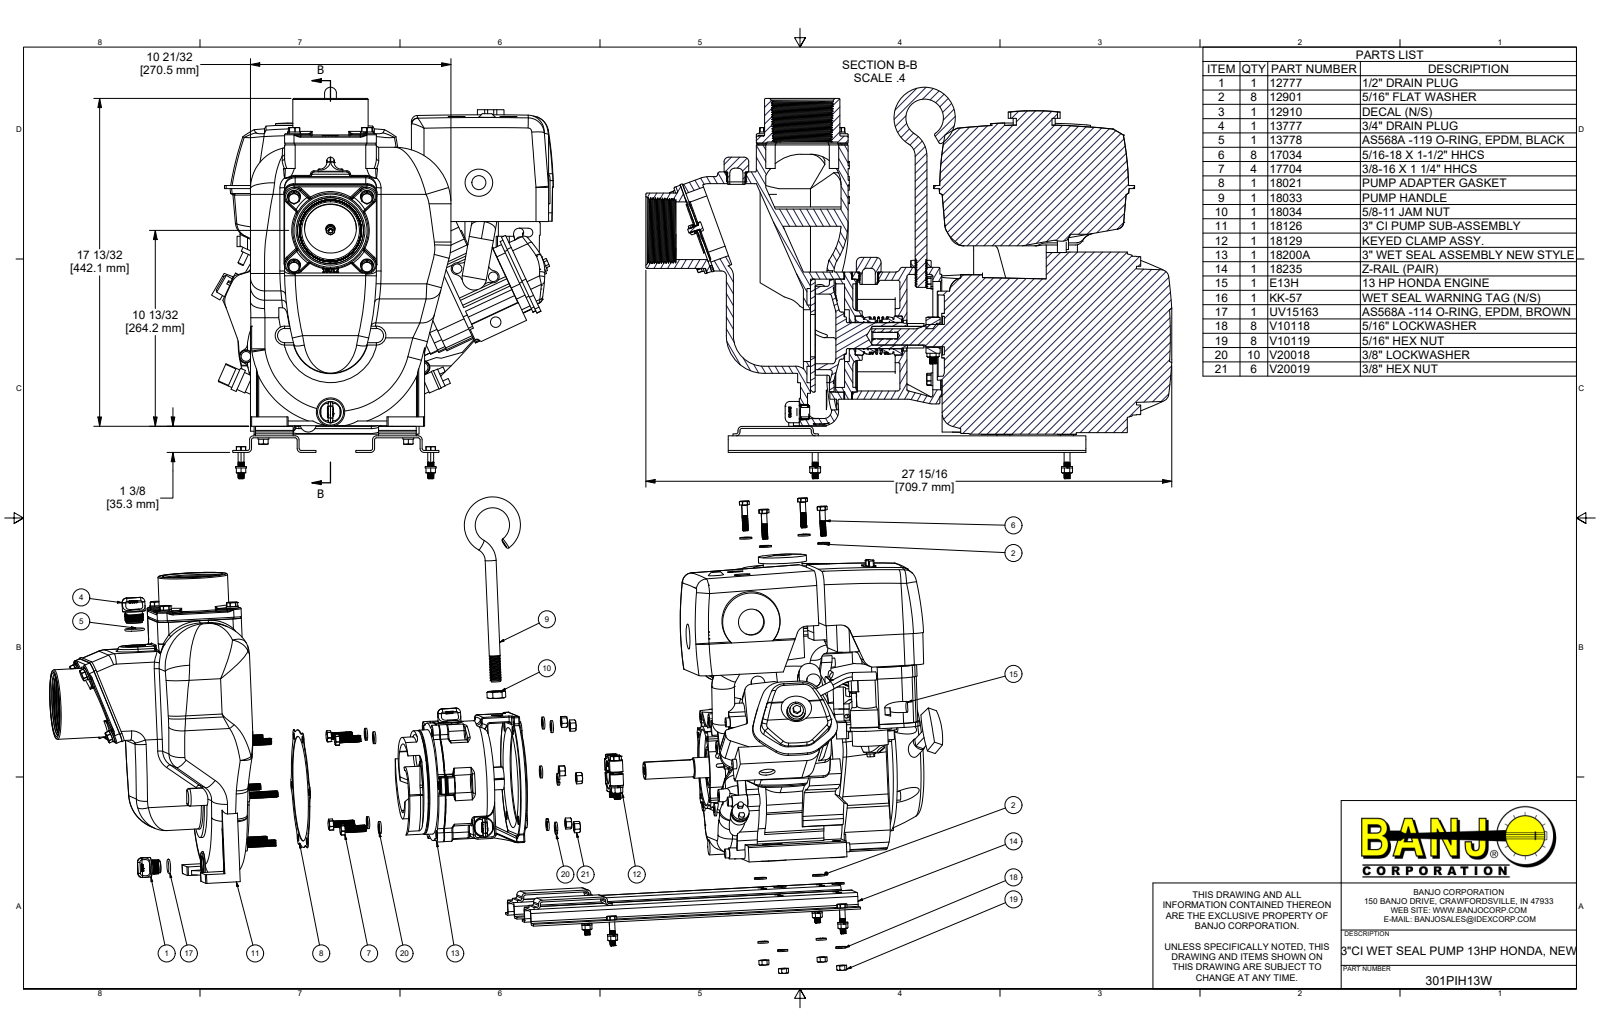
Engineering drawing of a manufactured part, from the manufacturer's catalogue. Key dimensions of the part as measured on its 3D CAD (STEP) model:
Part name (STEP PRODUCT): 301PIH13W; 18126; 18001; 18004 (+8 more)
STEP written by: Autodesk Inventor 2019 (AUTOMOTIVE_DESIGN)
Units: inches
Bodies: 118 solids, 10653 faces (2381 planar, 3752 cylindrical, 4520 other)
Overall size (bounding box): 56.392 × 20.781 × 20.741
Volume: 2 372 in³ · Surface area: 6 538 in²
Round holes (diameter × count): ⌀0.385 ×20, ⌀0.375 ×18, ⌀0.406 ×18, ⌀0.307 ×16, ⌀0.344 ×10, ⌀0.437 ×10, ⌀0.252 ×8, ⌀0.307 ×8, ⌀0.322 ×8, ⌀0.315 ×6, ⌀0.469 ×4, ⌀0.5 ×3
Round bosses / shafts (diameter × count): ⌀0.324 ×272, ⌀0.268 ×120, ⌀0.687 ×20, ⌀0.512 ×17, ⌀0.375 ×16, ⌀0.212 ×12, ⌀0.583 ×8, ⌀0.313 ×8
Partial cylindrical surfaces — rounded edges, fillets, slot ends (radius × count): R0.06 ×82, R0.03 ×56, R0.25 ×46, R0.787 ×43, R0.394 ×35, R0.162 ×32, R0.125 ×31, R0.375 ×29
Main face-to-face distances: 0.105, 0.375, 0.104, 0.671, 0.775, 0.776, 0.88, 0.085, 0.965, 0.86
Hole centre spacings: 3.875, 5.48, 3.375, 6.75, 6.536, 6.536, 2.351, 2.74
